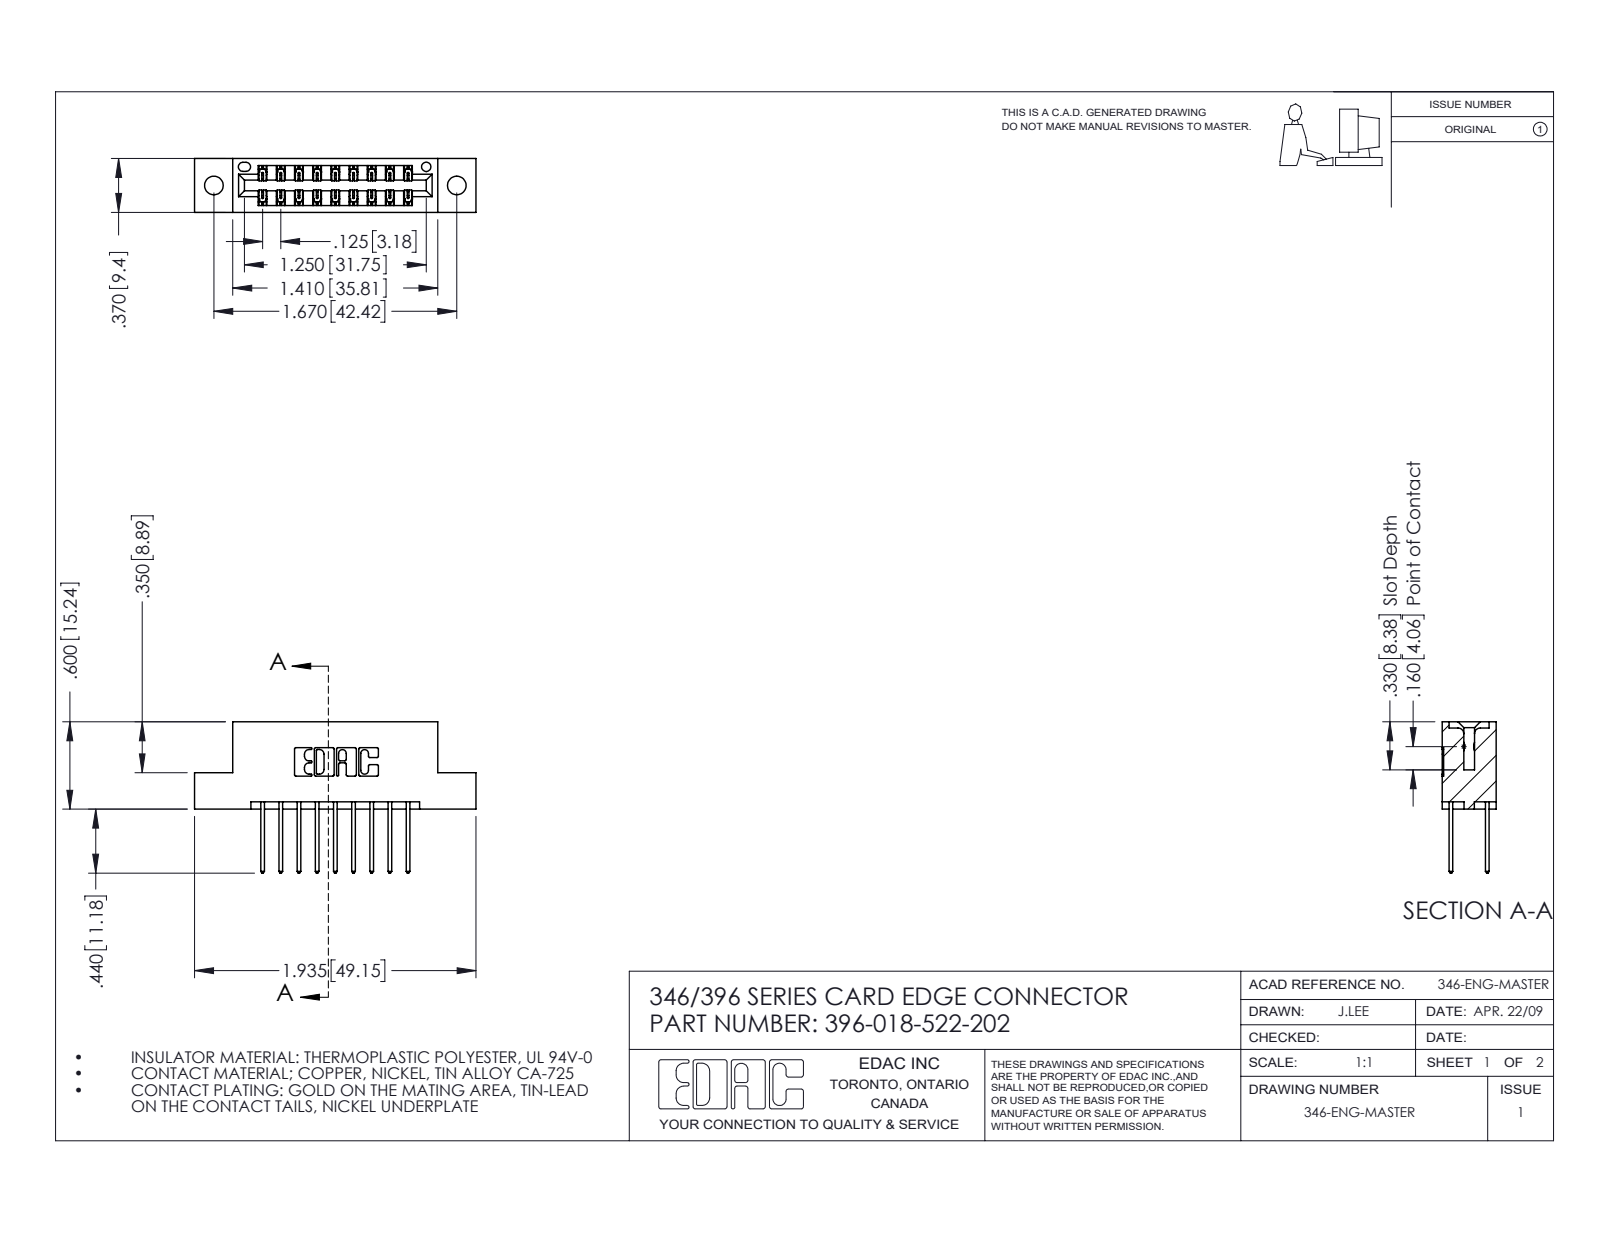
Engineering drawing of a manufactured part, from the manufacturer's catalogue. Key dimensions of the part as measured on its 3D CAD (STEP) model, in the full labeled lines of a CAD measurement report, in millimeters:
Part name (STEP PRODUCT): 346 Part_Flush Mounting Lugs - 0.128 Dia; 396-018-522-202; 345-292-001_345-293-122
STEP written by: SolidWorks 2016 (CONFIG_CONTROL_DESIGN)
Units: millimetres
Bodies: 19 solids, 1058 faces (706 planar, 352 cylindrical, 0 other)
Overall size (bounding box): 49.1 × 26.4 × 9.4
Volume: 4 540 mm³ · Surface area: 5 674 mm²
Round holes (diameter × count): ⌀3.3 ×2, ⌀1.6 ×1
Partial cylindrical surfaces — rounded edges, fillets, slot ends (radius × count): R0.2 ×27, R0.3 ×22, R0.3 ×18, R0.2 ×6, R0.8 ×6, R0.7 ×3, R0.4 ×2, R0.6 ×2
Main face-to-face distances: 6.4, 1.2, 8.2, 9.4, 1.8, 7.6, 0.6, 7, 3.8, 5.6
Hole centre spacings: 6.2, 37.2, 42.4
